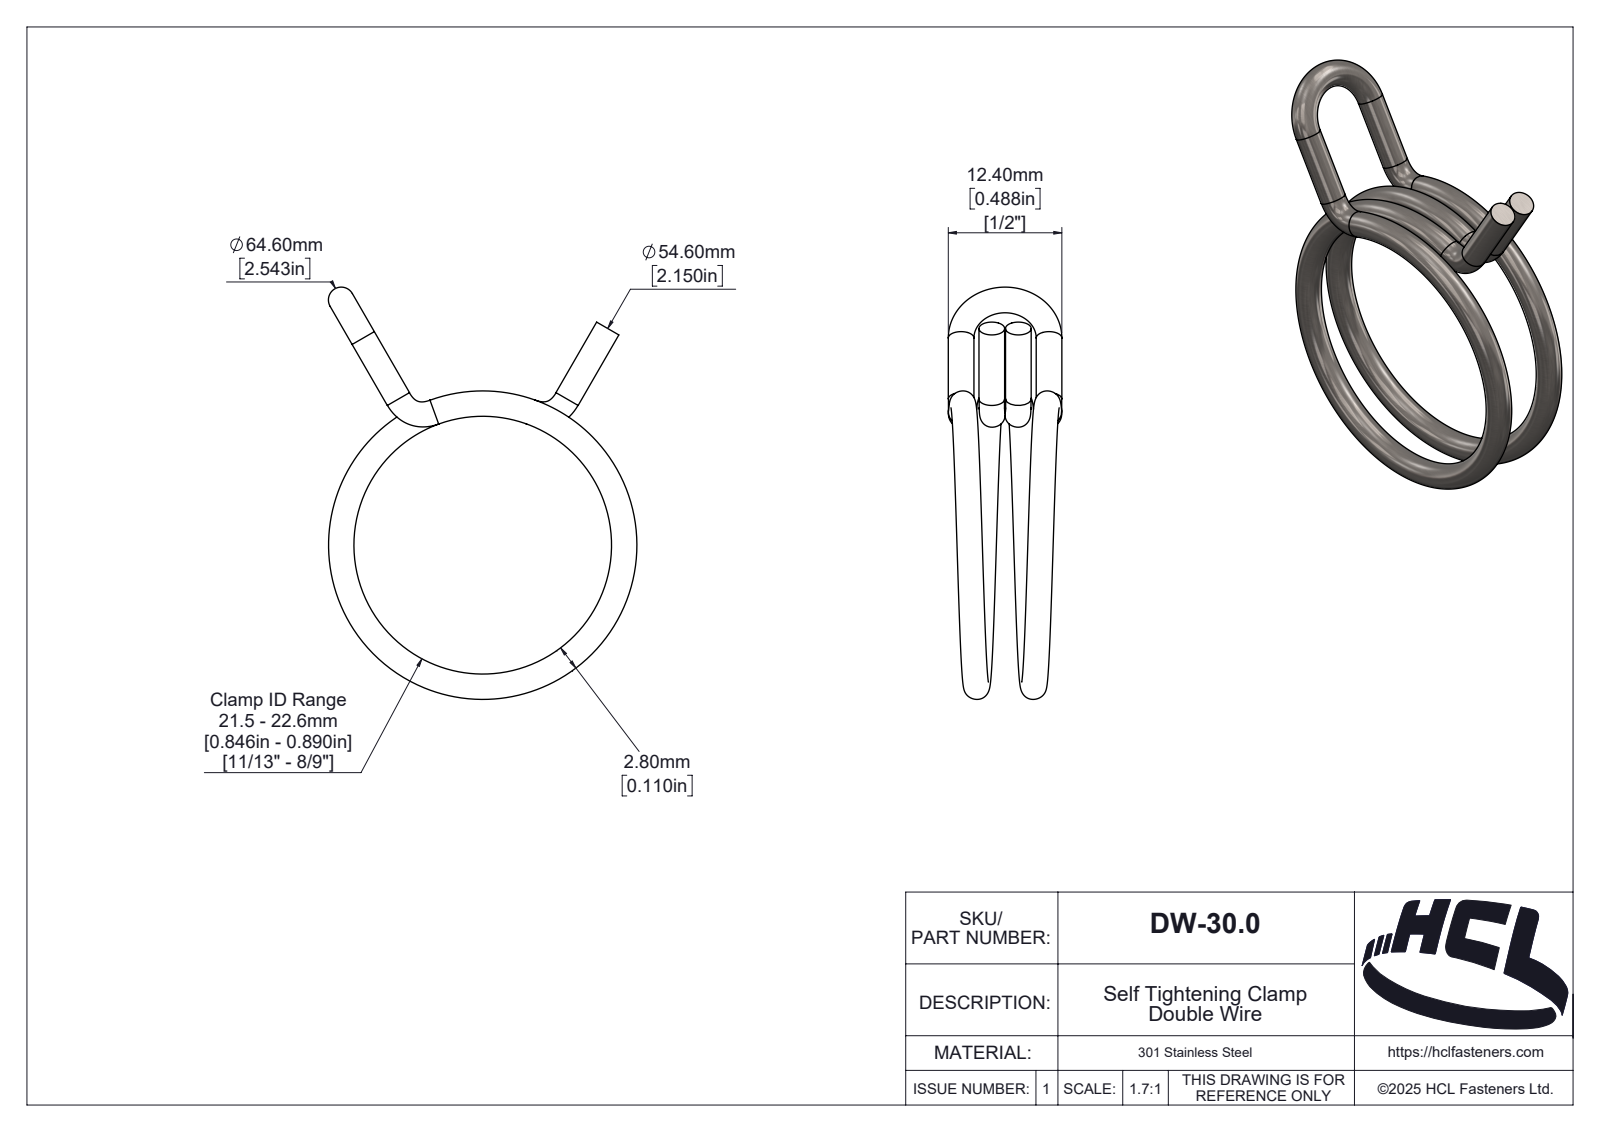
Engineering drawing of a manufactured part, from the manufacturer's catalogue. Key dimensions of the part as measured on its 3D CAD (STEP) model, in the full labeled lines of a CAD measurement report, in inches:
Part name (STEP PRODUCT): DW-30.0
STEP written by: SolidWorks 2025 (AUTOMOTIVE_DESIGN)
Units: inches
Bodies: 1 solid, 132 faces (14 planar, 53 cylindrical, 65 other)
Overall size (bounding box): 1.771 × 1.326 × 0.488
Volume: 0.105 in³ · Surface area: 3.846 in²
Round bosses / shafts (diameter × count): ⌀0.11 ×4
Partial cylindrical surfaces — rounded edges, fillets, slot ends (radius × count): R0.006 ×1, R0.008 ×1, R0.008 ×1, R0.01 ×1, R0.014 ×1, R0.019 ×1, R0.024 ×1, R0.027 ×1
